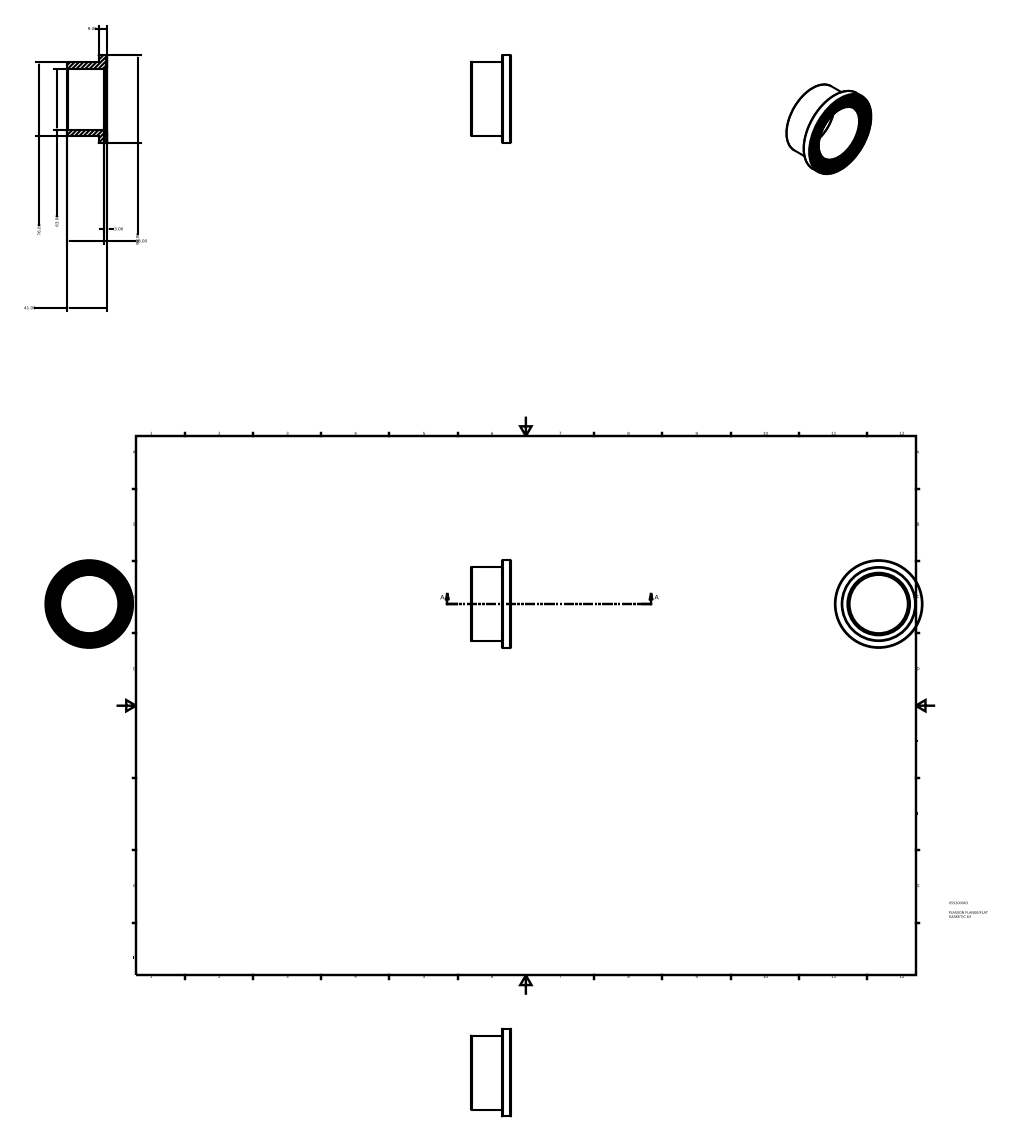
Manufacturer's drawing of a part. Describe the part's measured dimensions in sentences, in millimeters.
The part is named "055200063". Its 3-D file was written by "Autodesk Inventor 2015 (AUTOMOTIVE_DESIGN)". It is 1 solid with 33 faces: 9 planar, 9 cylindrical and 15 other. Overall it measures 90 by 90 by 41 millimeters. Its volume is 73 111 cubic millimeters and its surface area 25 743 square millimeters. Round holes: 1 of diameter 59.85, 1 of diameter 63, 1 of diameter 64.88, 1 of diameter 74.92, 1 of diameter 84.97. Round bosses or shafts: 1 of diameter 90, 1 of diameter 79.95, 1 of diameter 76, 1 of diameter 69.9. The main face-to-face distances are 32, 41, 9, 39.65, 7.65, 1.35, 38, 6, 1.65, 3.
